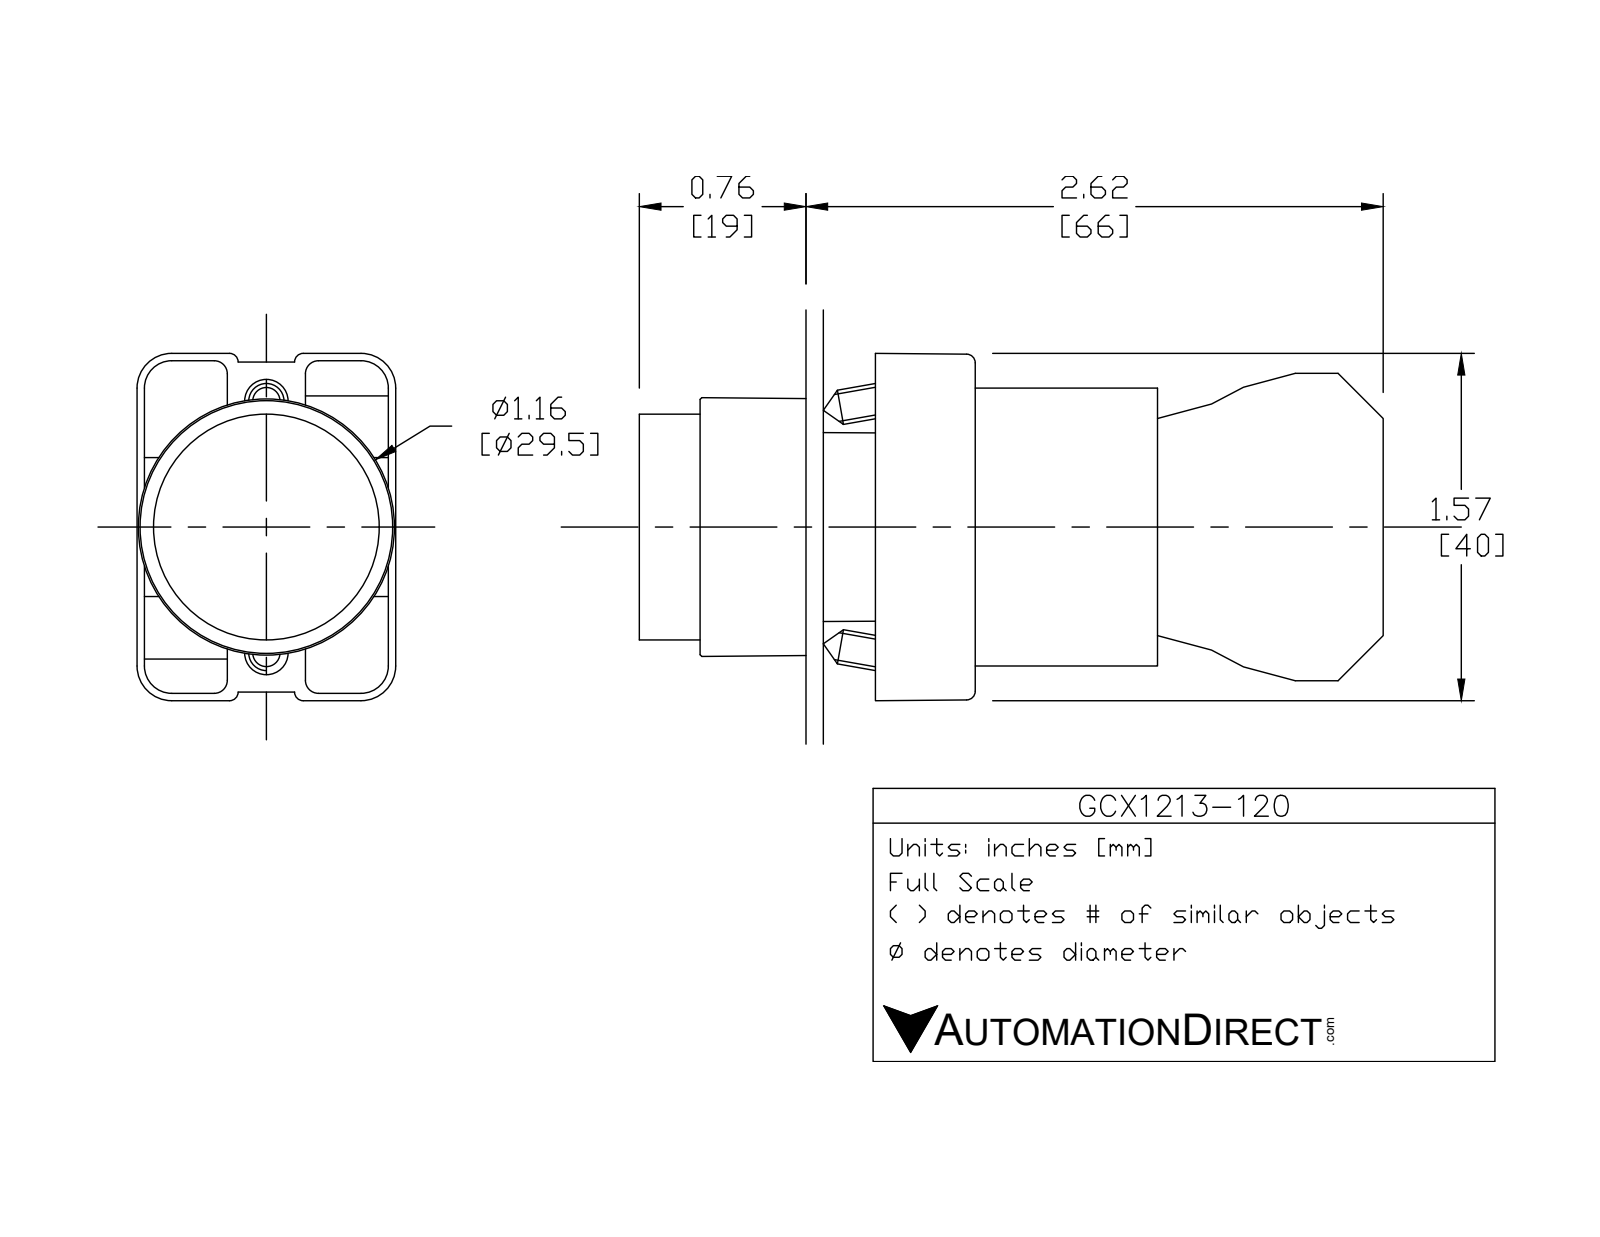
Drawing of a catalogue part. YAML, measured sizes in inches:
part_name: "GCX1213-120; ecx1040; GCX1213 OPERATOR; ecx1029 (+1 more)"
step_written_by: "SolidWorks 2016 (AUTOMOTIVE_DESIGN)"
units: inches
bodies: {solids: 7, faces: 425, planar: 250, cylindrical: 144, other: 31}
overall_size: [3.319, 1.581, 1.177]
volume: 2.721
surface_area: 36.32
round_holes:
  - {diameter: 0.079, count: 2}
  - {diameter: 0.124, count: 2}
  - {diameter: 0.13, count: 2}
  - {diameter: 0.087, count: 1}
  - {diameter: 0.197, count: 1}
  - {diameter: 0.469, count: 1}
  - {diameter: 0.878, count: 1}
  - {diameter: 0.888, count: 1}
  - {diameter: 1.024, count: 1}
round_bosses_or_shafts:
  - {diameter: 0.157, count: 4}
  - {diameter: 1.175, count: 1}
  - {diameter: 1.004, count: 1}
  - {diameter: 0.945, count: 1}
  - {diameter: 0.856, count: 1}
  - {diameter: 0.78, count: 1}
  - {diameter: 0.504, count: 1}
partial_cylinders:
  - {radius: 0.059, count: 24}
  - {radius: 0.041, count: 12}
  - {radius: 0.124, count: 12}
  - {radius: 0.157, count: 12}
  - {radius: 0.039, count: 8}
  - {radius: 0.128, count: 2}
  - {radius: 0.02, count: 1}
  - {radius: 0.063, count: 1}
face_to_face_distances: [0.827, 0.579, 1.171, 2.02, 1.193, 0.031, 0.033, 0.573, 1.165, 0.593]
hole_center_spacings: [0.236, 0.544, 0.472, 0.49]
